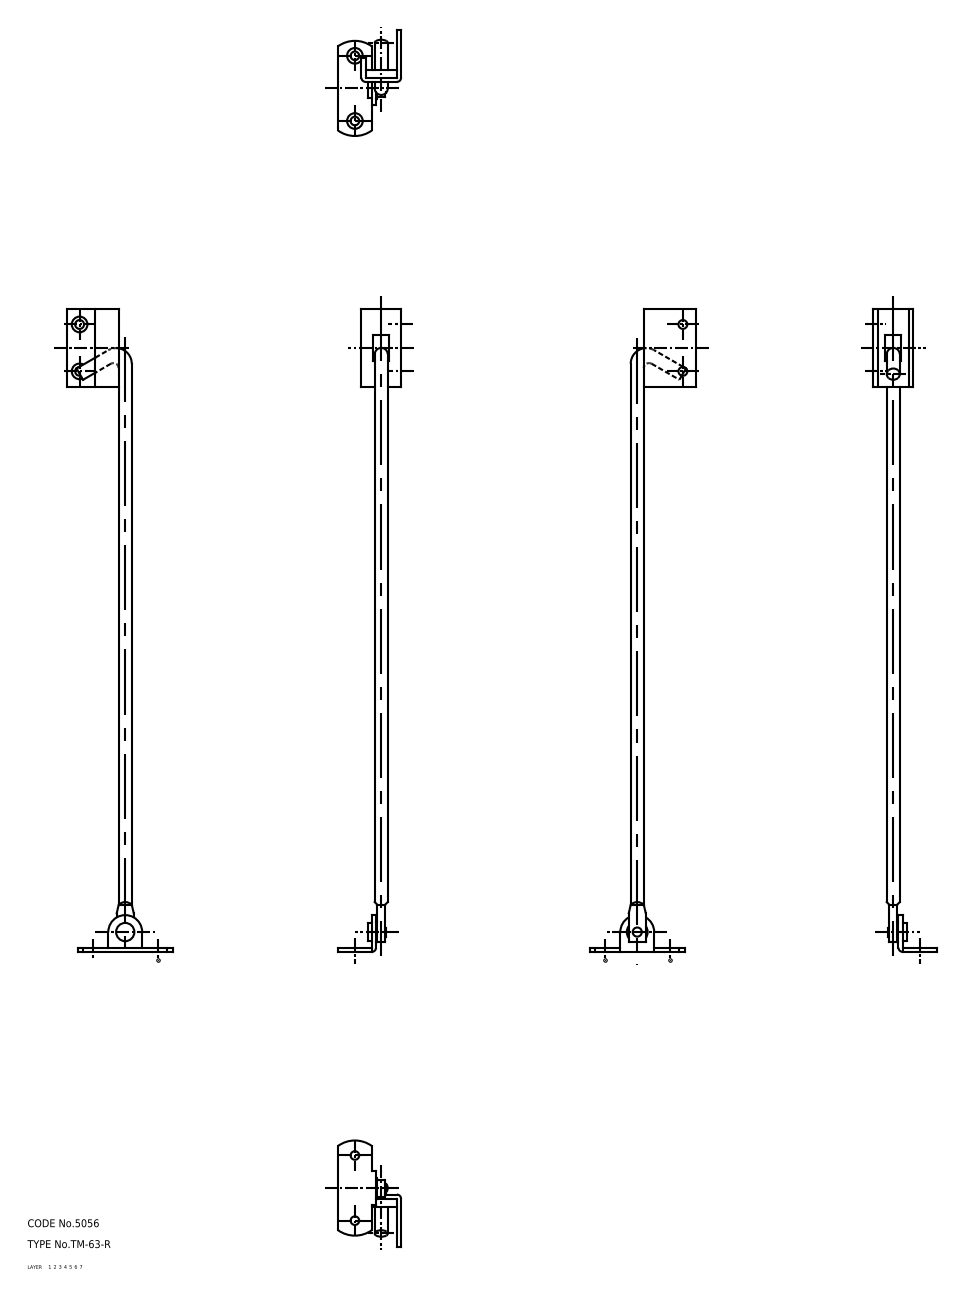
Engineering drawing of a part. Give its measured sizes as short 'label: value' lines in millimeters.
name: washer_mr; stopper_mr; rivet_mr; cushion_mr (+3 more)
written by: CADfix (AUTOMOTIVE_DESIGN)
unit: mm
bodies: 6 solids, 91 faces (0 planar, 0 cylindrical, 91 other)
size: 246.66 × 40.75 × 24.2
volume: 8 394 mm³; area: 9 066 mm²
